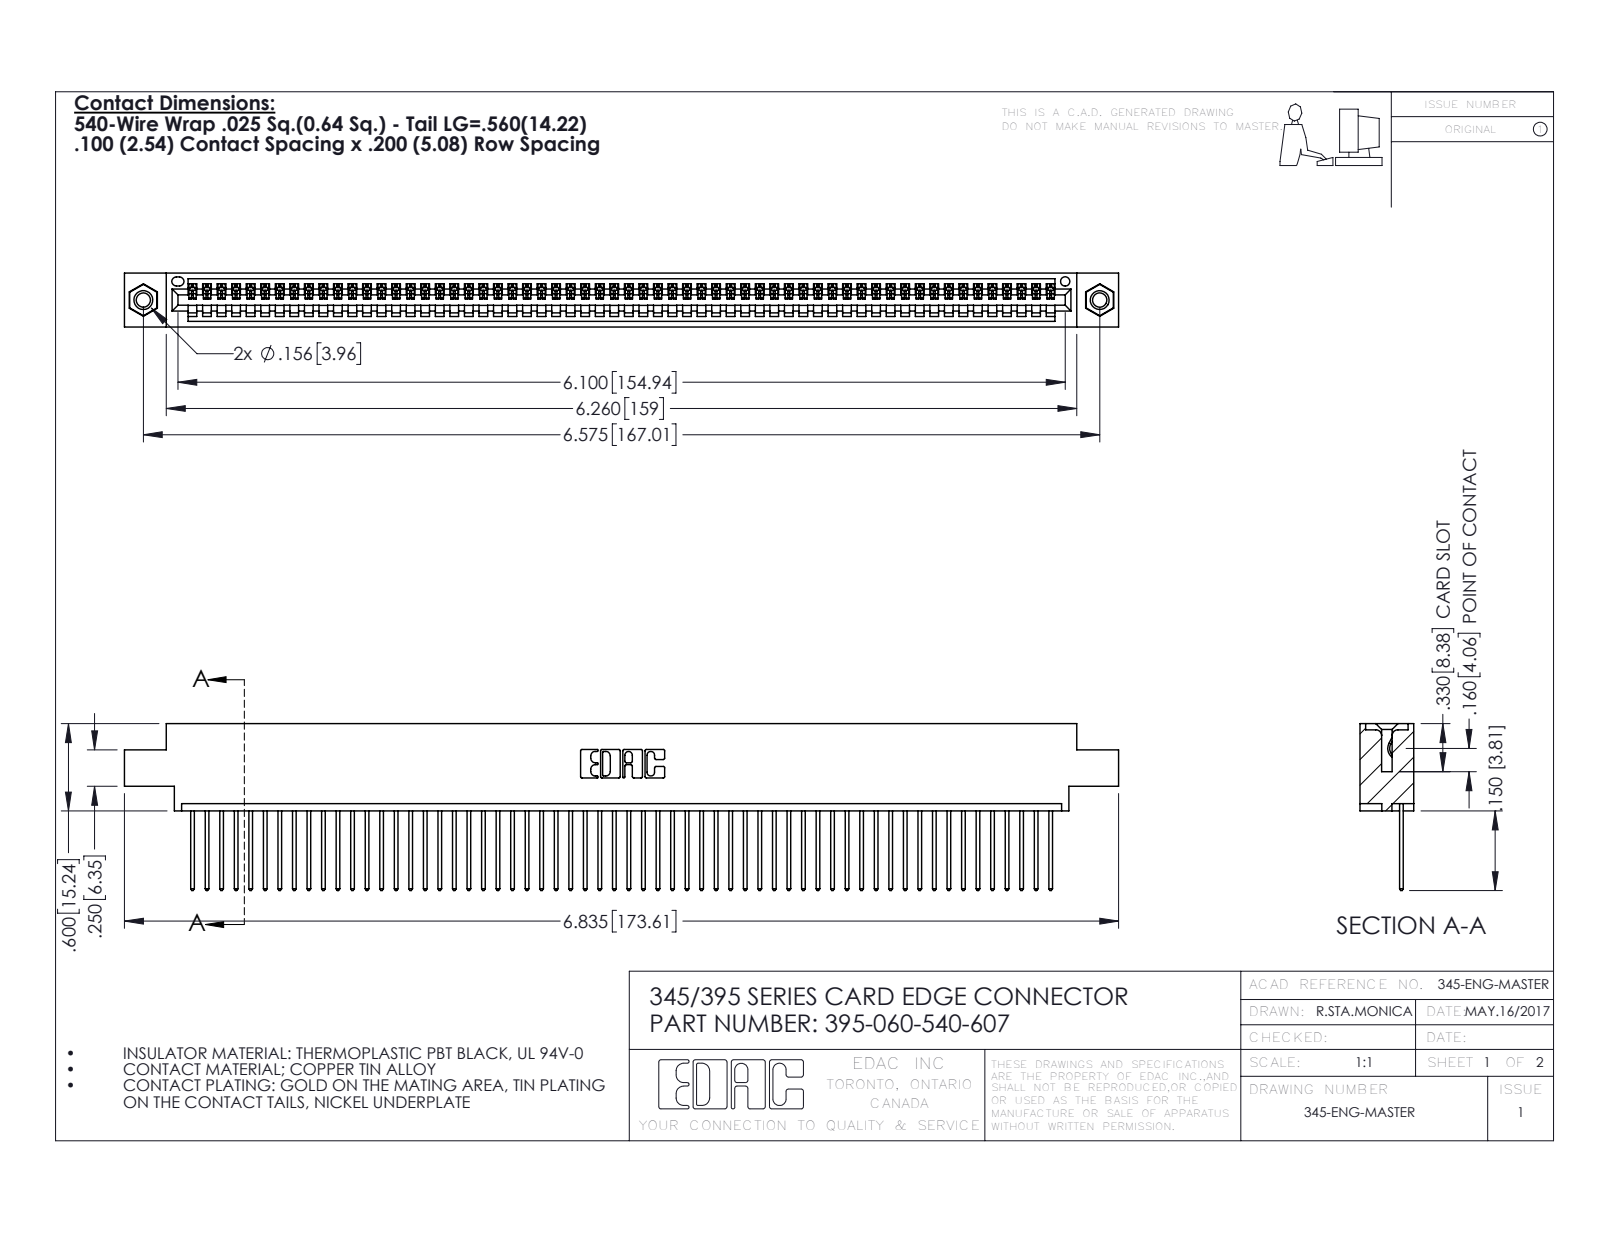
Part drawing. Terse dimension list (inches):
name: 345 Part_0.170 Offset - 0.156 Dia-TI; 395-060-540-607; 345-250-001_345-250-005-103; 345-292-001_345-293-140
written by: SolidWorks 2016 (CONFIG_CONTROL_DESIGN)
unit: in
bodies: 63 solids, 3670 faces (2516 planar, 1138 cylindrical, 16 other)
size: 6.835 × 1.147 × 0.37
volume: 1.012 in³; area: 35.71 in²
holes: 2× ⌀0.098, 2× ⌀0.125, 2× ⌀0.156, 1× ⌀0.064
bosses: 2× ⌀0.155
rounds: 120× R0.006, 120× R0.01, 22× R0.01, 6× R0.007, 6× R0.031, 3× R0.026, 2× R0.031, 2× R0.04
face distances: 0.072, 0.298, 0.37, 0.098, 0.272, 0.025, 0.2, 0.225, 0.175, 0.149
hole spacings: 0.27, 6.339, 6.575
